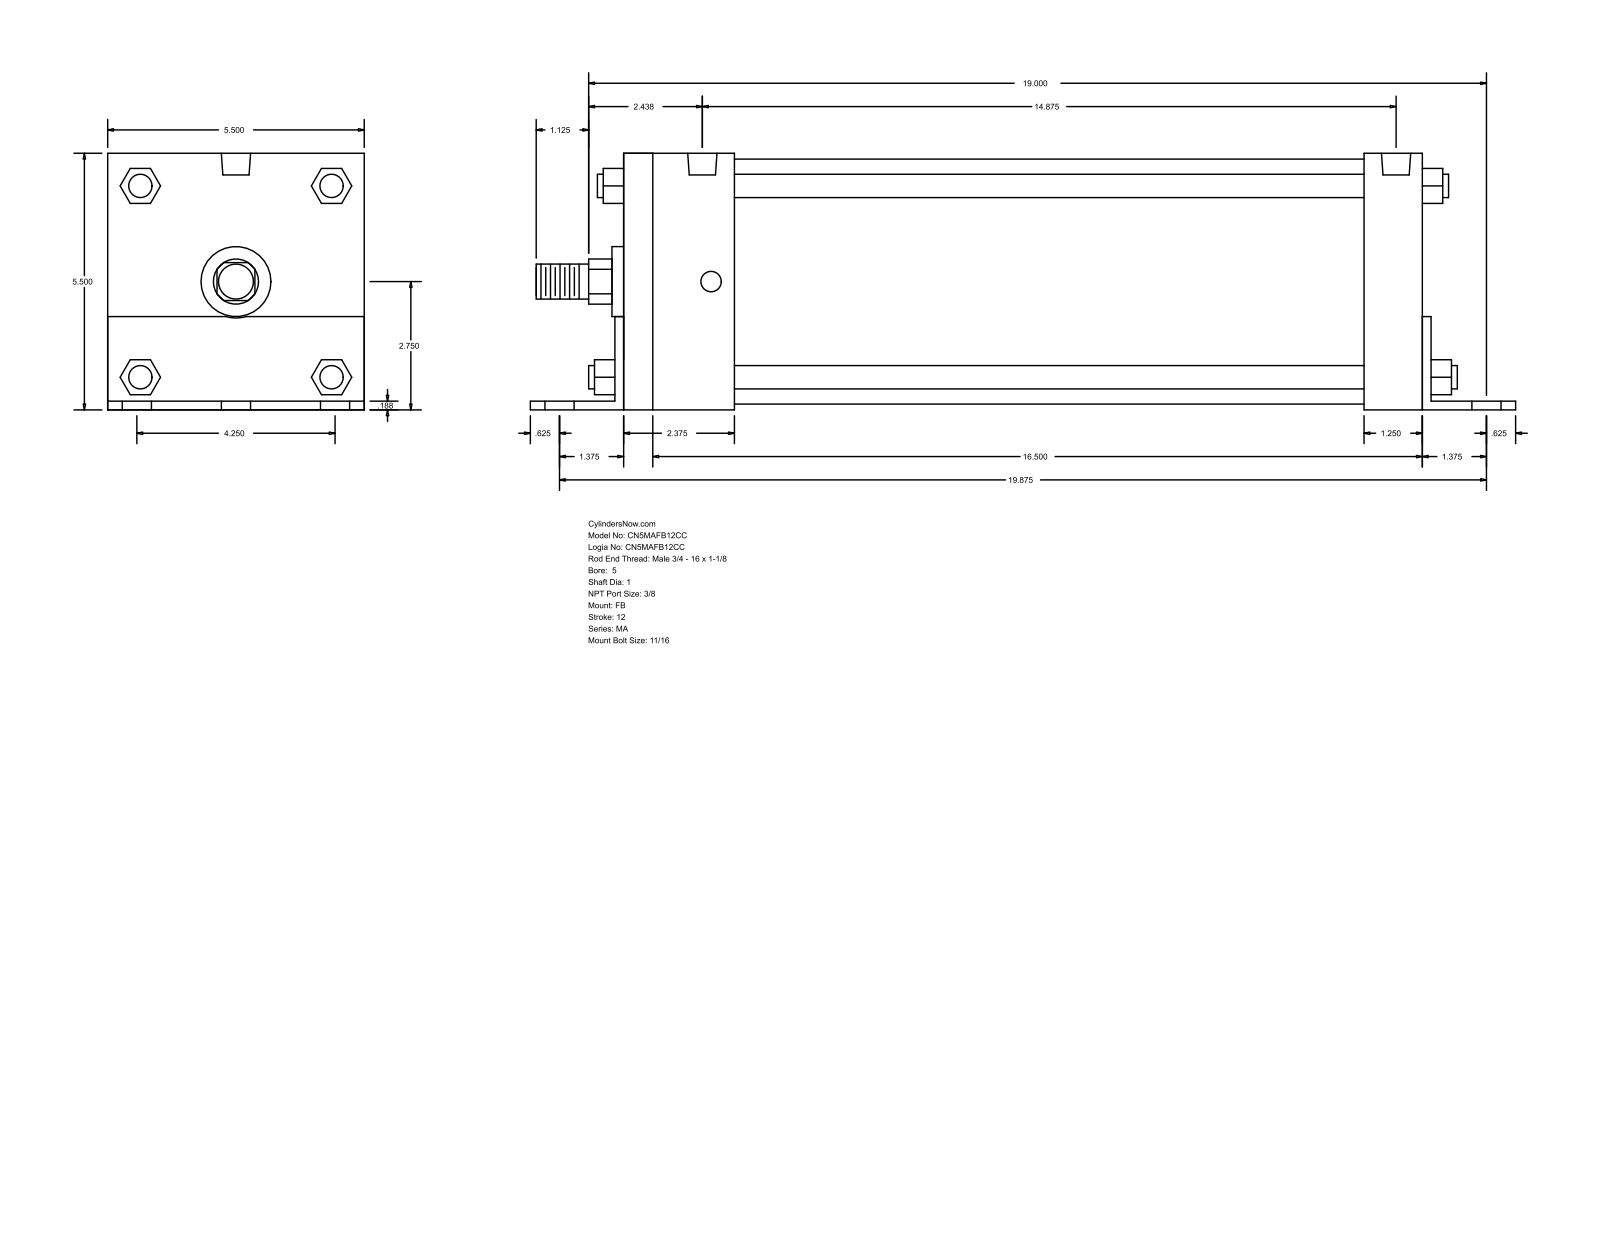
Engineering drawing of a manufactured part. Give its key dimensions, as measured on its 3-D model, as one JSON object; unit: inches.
{"part_name": "MA_FB__0500_1", "step_written_by": "GSSL Pune (CONFIG_CONTROL_DESIGN)", "units": "inches", "bodies": {"solids": 0, "faces": 140, "planar": 105, "cylindrical": 35, "other": 0}, "overall_size": [21.125, 5.502, 5.5], "round_holes": [[0.687, 6], [0.437, 4], [0.627, 2]], "round_bosses_or_shafts": [[0.5, 4], [5.25, 1], [1.5, 1], [1, 1], [0.75, 1]], "partial_cylinders_radius": [[0.484, 1], [0.78, 1]], "face_to_face_distances": [5.5, 0.187, 5.502, 0.185, 5.315, 17.125, 0.188, 17.313, 17.312, 17.5], "hole_center_spacings": [2.125, 19.989, 19.875, 0.187, 2.876, 3.005, 3.728, 3.883]}
